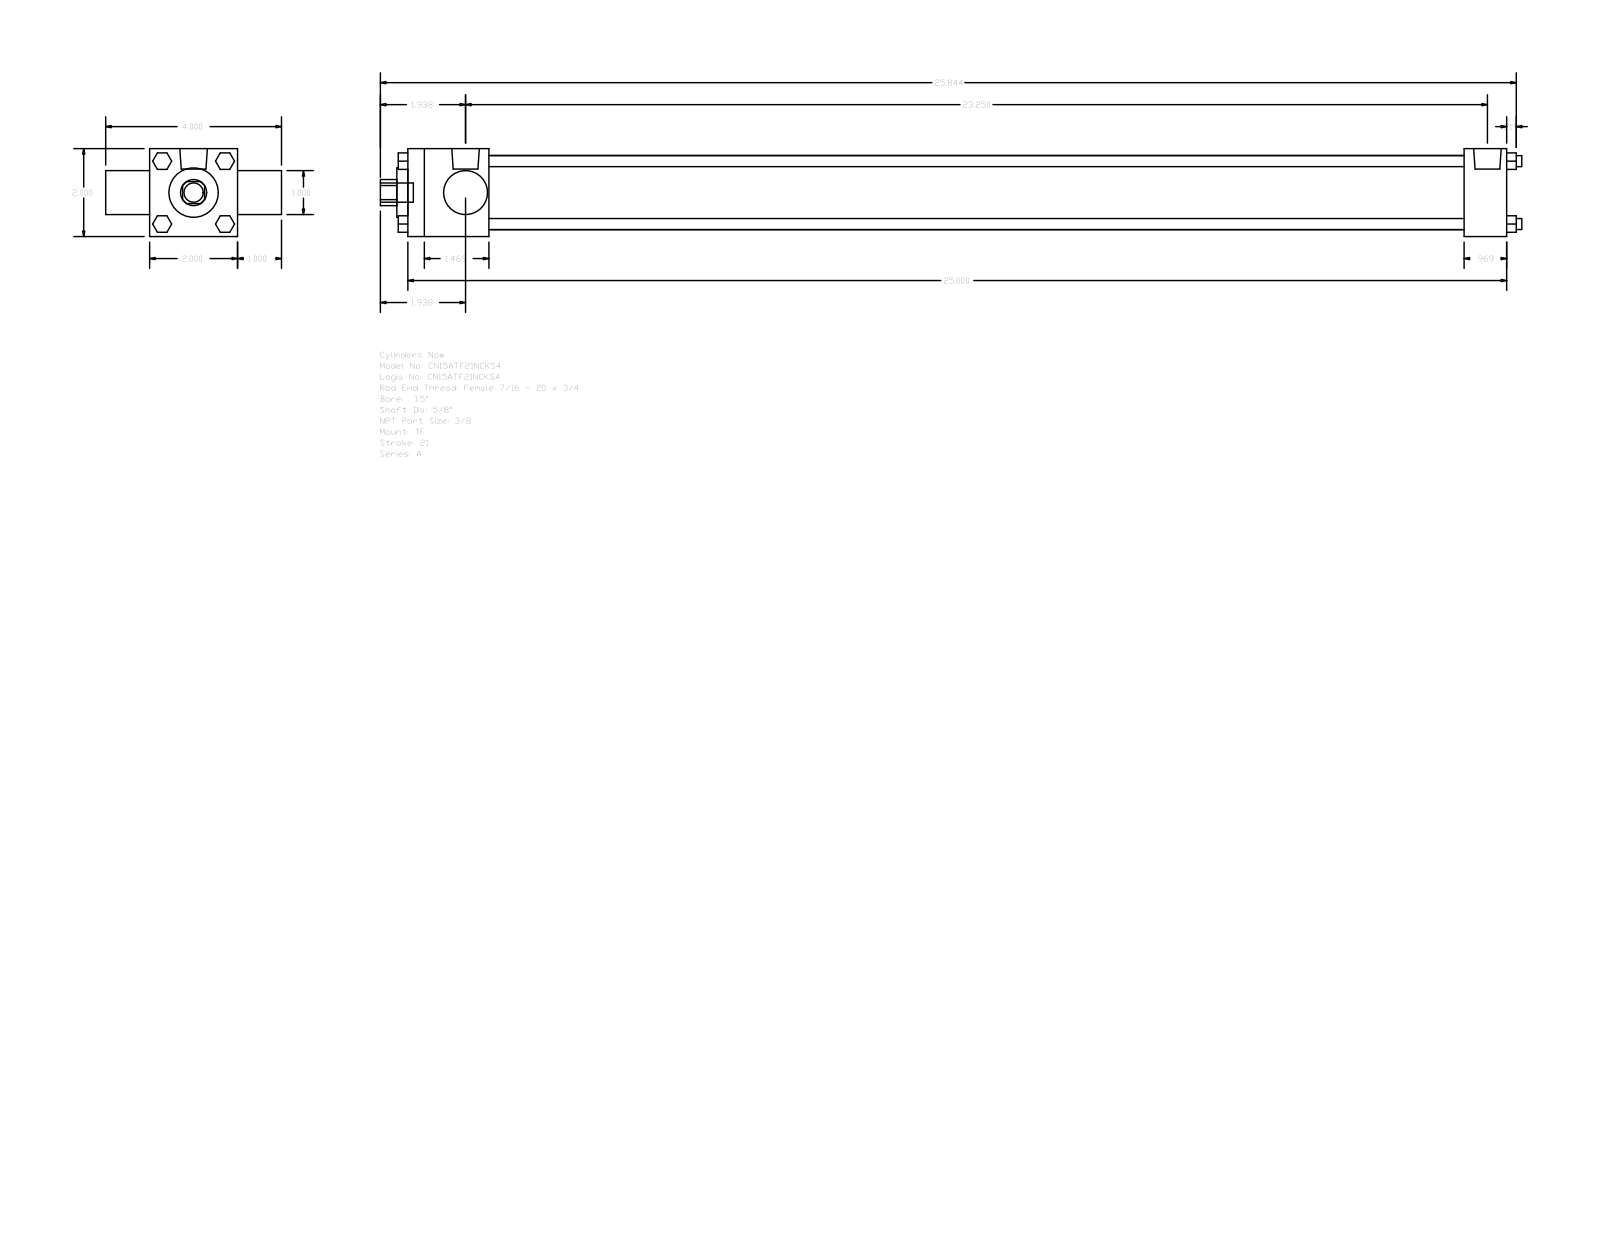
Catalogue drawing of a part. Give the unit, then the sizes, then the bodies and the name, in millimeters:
Units: millimetres
Overall size (bounding box): 659.61 × 101.6 × 50.8
Round holes (diameter × count): ⌀15.88 ×1, ⌀25.4 ×1, ⌀28.57 ×1, ⌀42.93 ×1
Round bosses / shafts (diameter × count): ⌀6.35 ×4, ⌀5.56 ×3, ⌀15.93 ×2, ⌀11.11 ×1
Partial cylindrical surfaces — rounded edges, fillets, slot ends (radius × count): R7.54 ×1
Main face-to-face distances: 50.8, 635, 25.4, 76.2, 46.83, 610.39, 563.56, 588.17, 24.61, 9.52
Bodies: 0 solids, 120 faces (92 planar, 28 cylindrical, 0 other)
Part name (STEP PRODUCT): A_TF__0150_0.625
STEP written by: GSSL Pune (CONFIG_CONTROL_DESIGN)
